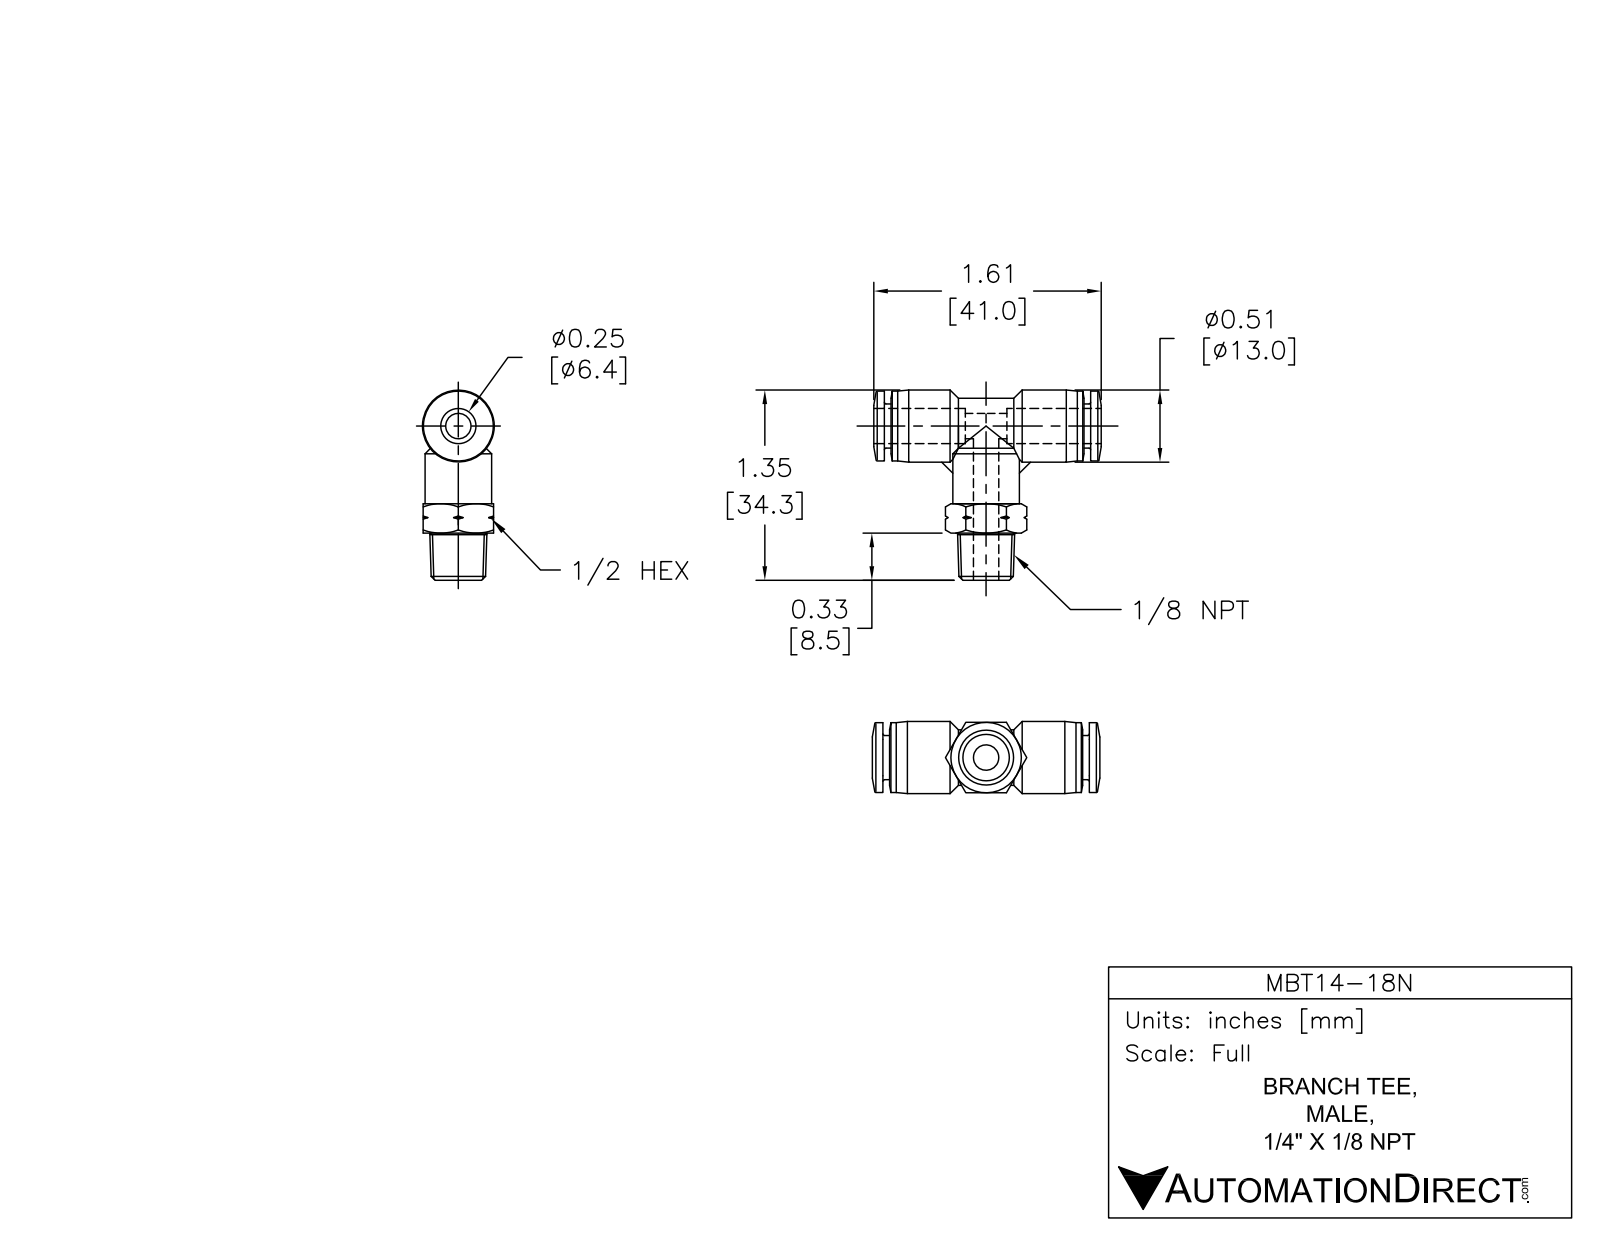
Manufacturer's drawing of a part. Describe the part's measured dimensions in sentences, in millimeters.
The part is named "MBT14-18N". Its 3-D file was written by "SolidWorks 2015 (AUTOMOTIVE_DESIGN)". It is 1 solid with 114 faces: 21 planar, 31 cylindrical and 62 other. Overall it measures 41 by 34.3 by 13 millimeters. Its volume is 5 330 cubic millimeters and its surface area 4 069 square millimeters. Round holes: 2 of diameter 4.5, 1 of diameter 6.6. Round bosses or shafts: 1 of diameter 13, 1 of diameter 12.6, 1 of diameter 12, 1 of diameter 10, 1 of diameter 8. Partial cylindrical surfaces (rounded edges, fillets, slot ends): 1 of radius 5. The main face-to-face distances are 12.7, 37.2, 1.2, 36, 8.5, 14.9, 22.3, 13.7, 21.1, 34.8.
